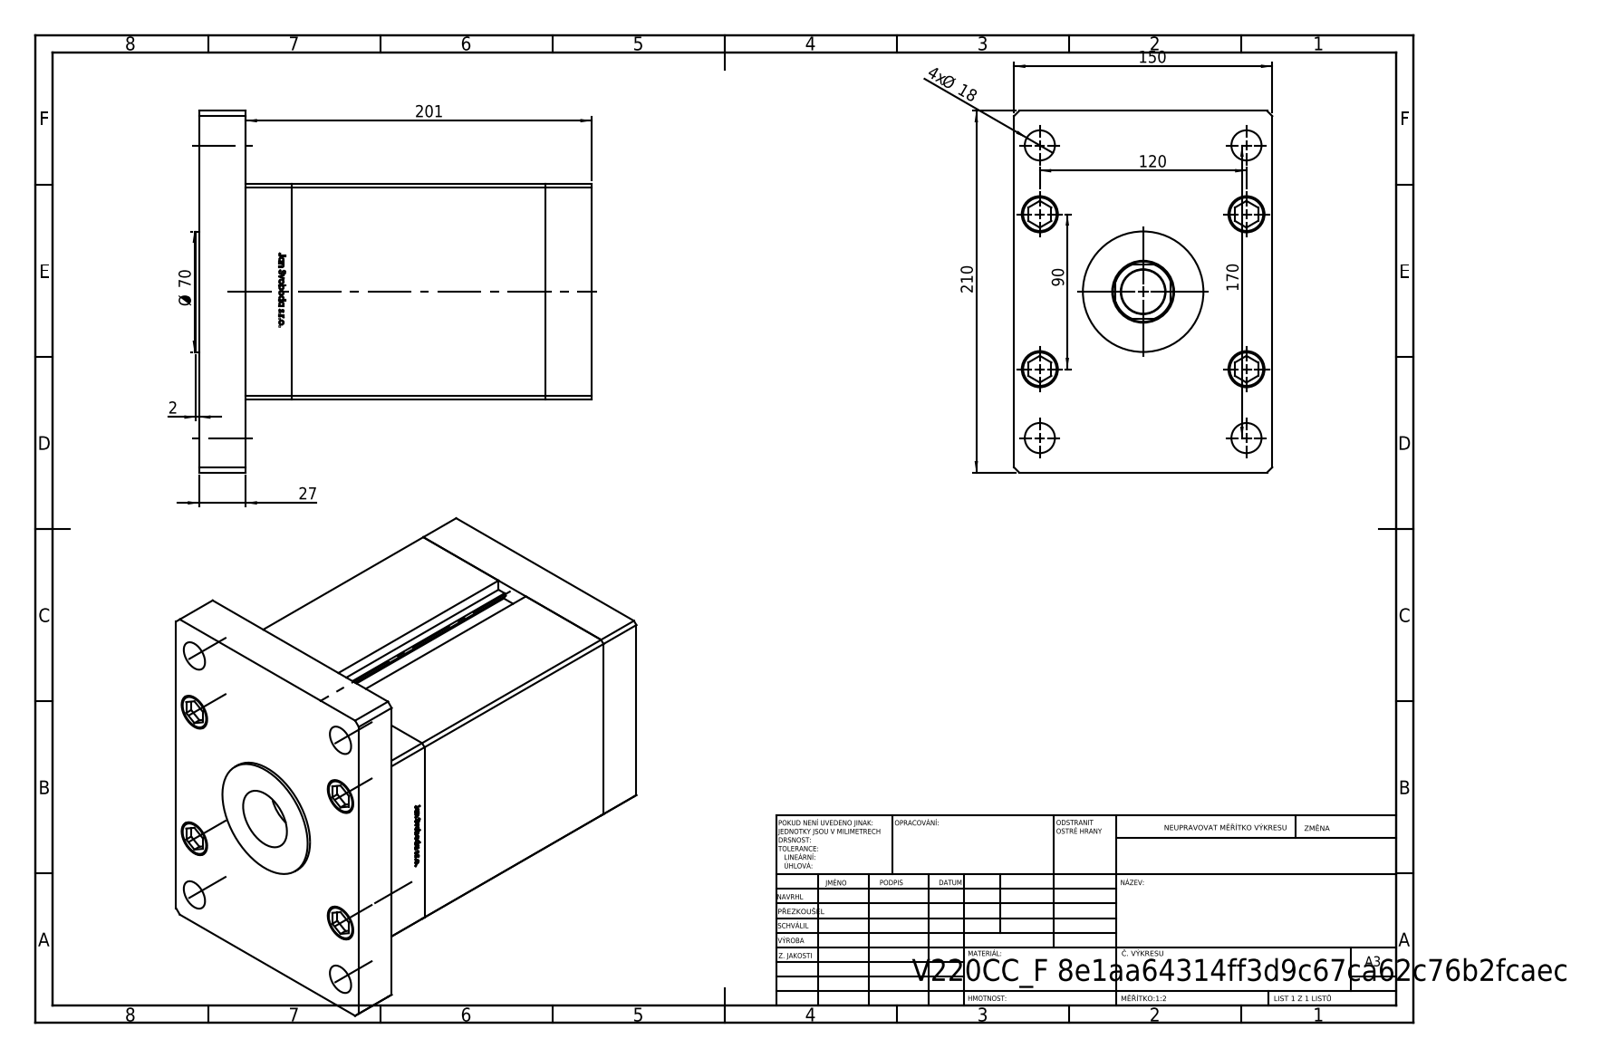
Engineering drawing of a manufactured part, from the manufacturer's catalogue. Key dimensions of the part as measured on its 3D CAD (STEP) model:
Part name (STEP PRODUCT): V220C_F; V220C BACK_F; ALLEN BOLT; V220C_VC_F (+2 more)
STEP written by: SolidWorks 2019 (CONFIG_CONTROL_DESIGN)
Units: millimetres
Bodies: 19 solids, 1298 faces (513 planar, 179 cylindrical, 606 other)
Overall size (bounding box): 230 × 210 × 150
Volume: 3 996 000 mm³ · Surface area: 444 622 mm²
Round holes (diameter × count): ⌀17.5 ×9, ⌀22 ×5, ⌀16 ×4, ⌀21 ×4, ⌀25.5 ×1, ⌀36 ×1, ⌀37.5 ×1
Round bosses / shafts (diameter × count): ⌀8 ×9, ⌀21 ×5, ⌀80 ×1, ⌀70 ×1
Partial cylindrical surfaces — rounded edges, fillets, slot ends (radius × count): R0.93 ×2, R17.5 ×1
Main face-to-face distances: 27, 174, 201, 150, 125, 147, 54, 228, 34.8, 7.8
Hole centre spacings: 51, 40, 75, 104.04, 120, 126.49, 130, 176.92
